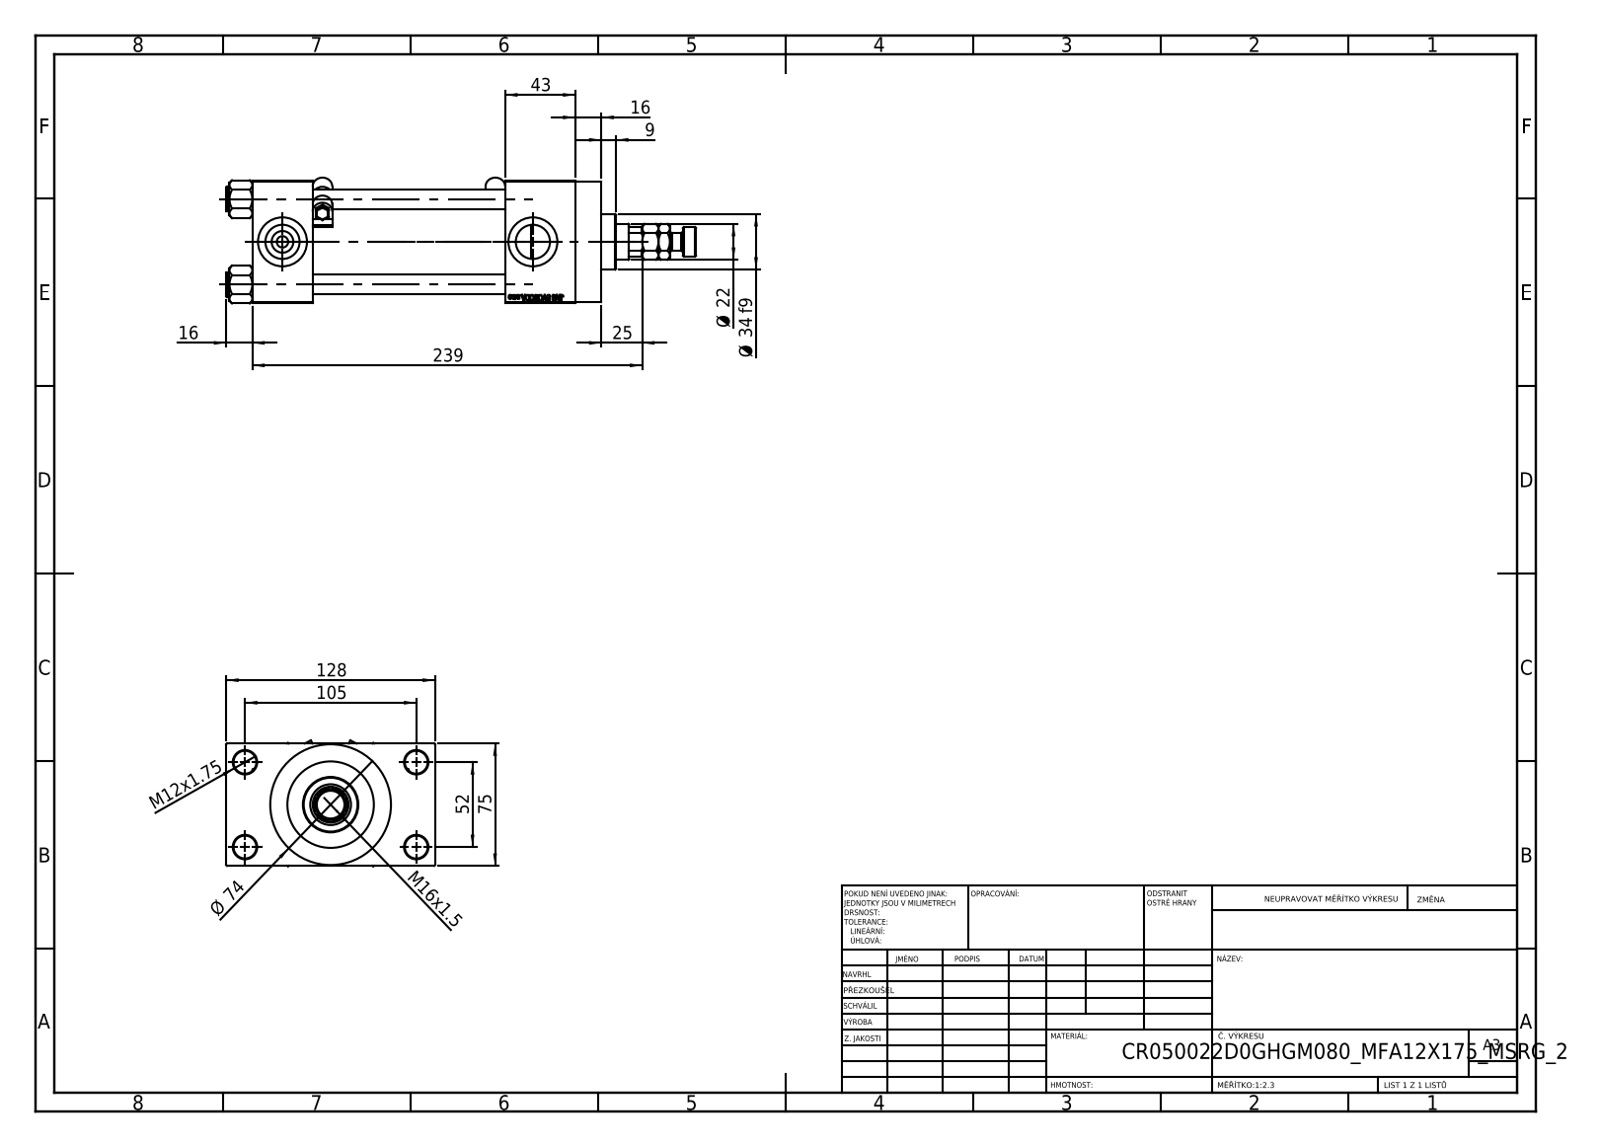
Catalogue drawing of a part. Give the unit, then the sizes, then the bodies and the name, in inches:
Units: inches
Overall size (bounding box): 11.339 × 5.039 × 3.037
Round holes (diameter × count): ⌀0.472 ×4, ⌀0.551 ×4, ⌀0.276 ×2, ⌀0.825 ×2, ⌀1.181 ×2, ⌀0.413 ×1, ⌀0.866 ×1, ⌀0.984 ×1, ⌀1.614 ×1, ⌀1.969 ×1, ⌀2.087 ×1
Round bosses / shafts (diameter × count): ⌀0.591 ×4, ⌀0.197 ×2, ⌀0.098 ×2, ⌀2.913 ×1, ⌀2.205 ×1, ⌀1.339 ×1, ⌀0.709 ×1, ⌀0.433 ×1
Partial cylindrical surfaces — rounded edges, fillets, slot ends (radius × count): R0.02 ×12, R0.236 ×4, R0.413 ×1
Main face-to-face distances: 2.953, 4.646, 1.457, 6.102, 1.043, 7.795, 6.339, 1.693, 3.996, 0.63
Hole centre spacings: 1.037, 1.456, 2.059, 2.3, 2.307, 3.096, 3.715, 2.047
Volume: 54.49 in³ · Surface area: 320.9 in²
Bodies: 14 solids, 1219 faces (549 planar, 120 cylindrical, 550 other)
Part name (STEP PRODUCT): V215CR_D_TYCINKA; V215_VC_A; V215CR_D_Body; V215CR_VCP_D (+3 more)
STEP written by: SolidWorks 2019 (CONFIG_CONTROL_DESIGN)
